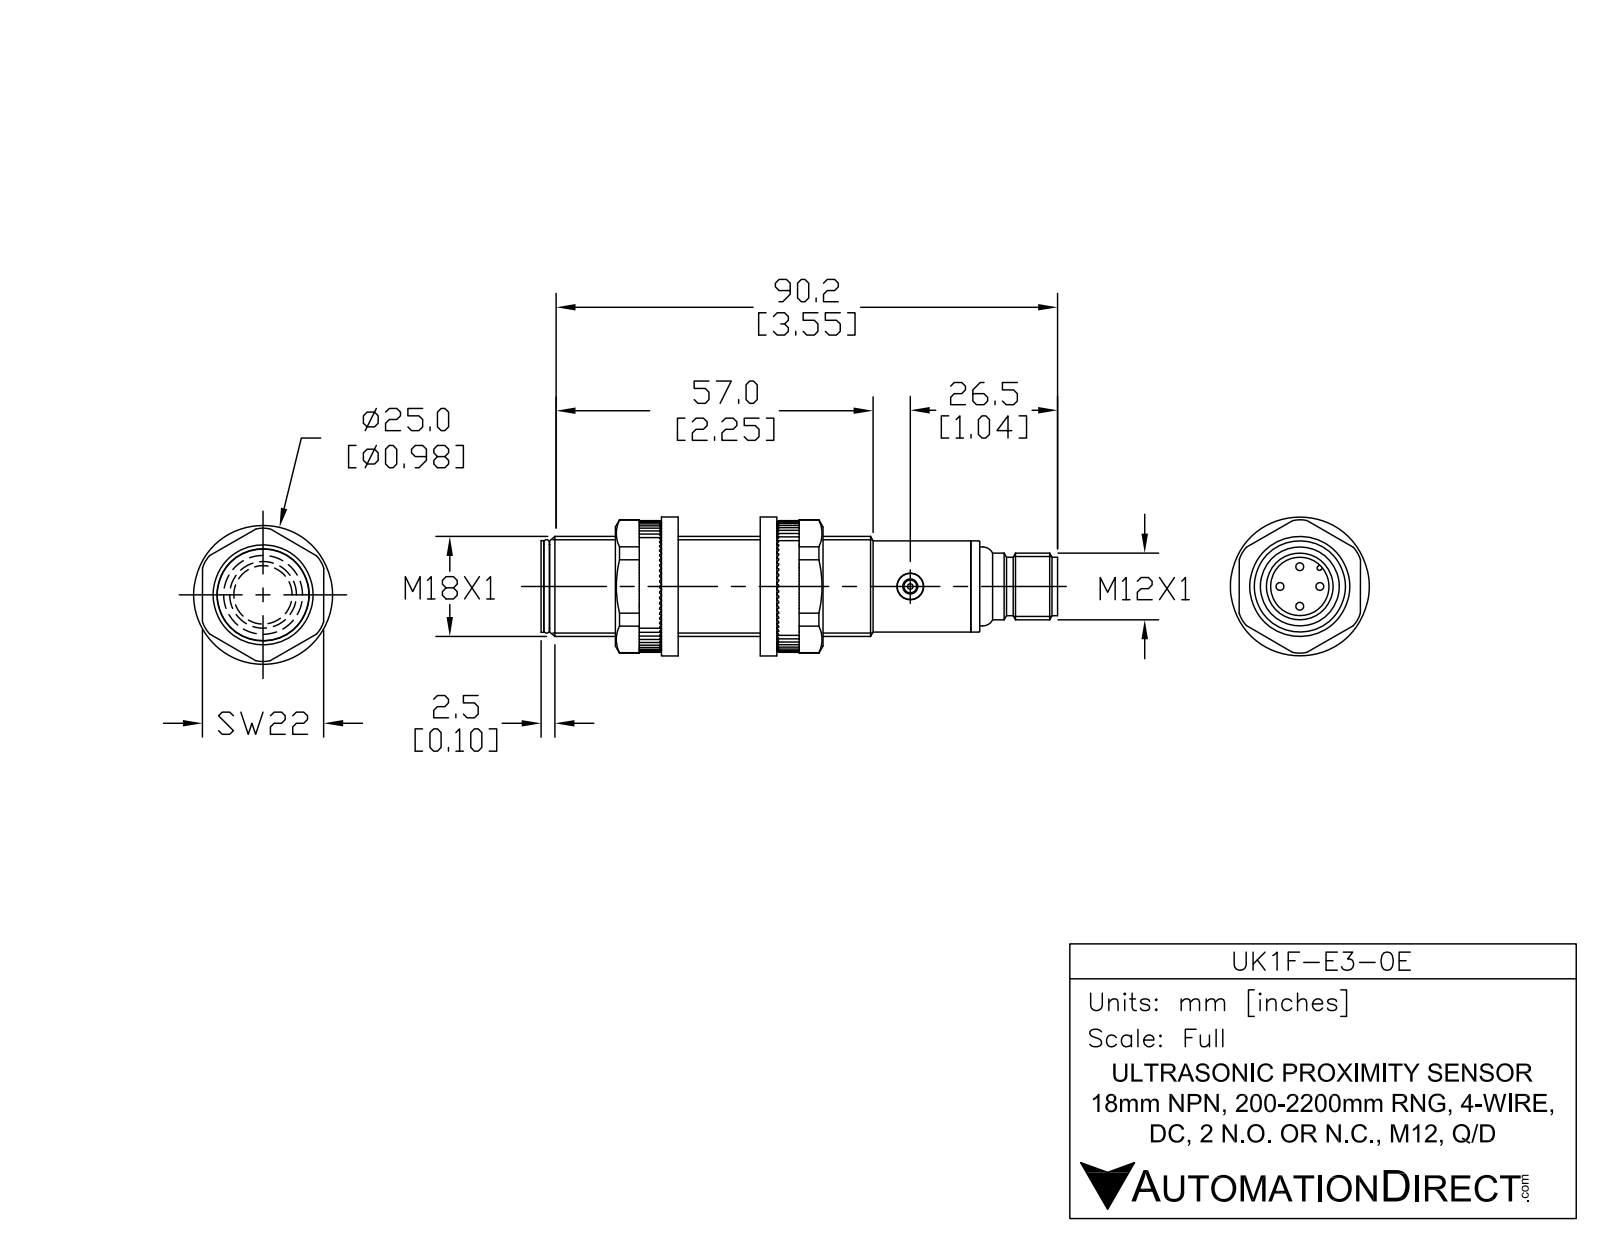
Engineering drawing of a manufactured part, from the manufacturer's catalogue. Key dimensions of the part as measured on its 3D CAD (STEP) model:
Part name (STEP PRODUCT): UK1F-E3-0E
STEP written by: SolidWorks 2017 (AUTOMOTIVE_DESIGN)
Units: inches
Bodies: 6 solids, 106 faces (21 planar, 48 cylindrical, 37 other)
Overall size (bounding box): 3.606 × 0.709 × 0.709
Volume: 1.202 in³ · Surface area: 10.68 in²
Round holes (diameter × count): ⌀0.106 ×1, ⌀0.185 ×1, ⌀0.276 ×1, ⌀0.327 ×1, ⌀0.374 ×1
Round bosses / shafts (diameter × count): ⌀0.039 ×4, ⌀0.709 ×1, ⌀0.654 ×1, ⌀0.646 ×1, ⌀0.622 ×1, ⌀0.559 ×1, ⌀0.472 ×1, ⌀0.413 ×1
Partial cylindrical surfaces — rounded edges, fillets, slot ends (radius × count): R0.024 ×1
Main face-to-face distances: 2.957, 0.039, 2.996, 0.037, 2.994, 0.043, 0.157, 3.055, 3.053, 3.016
